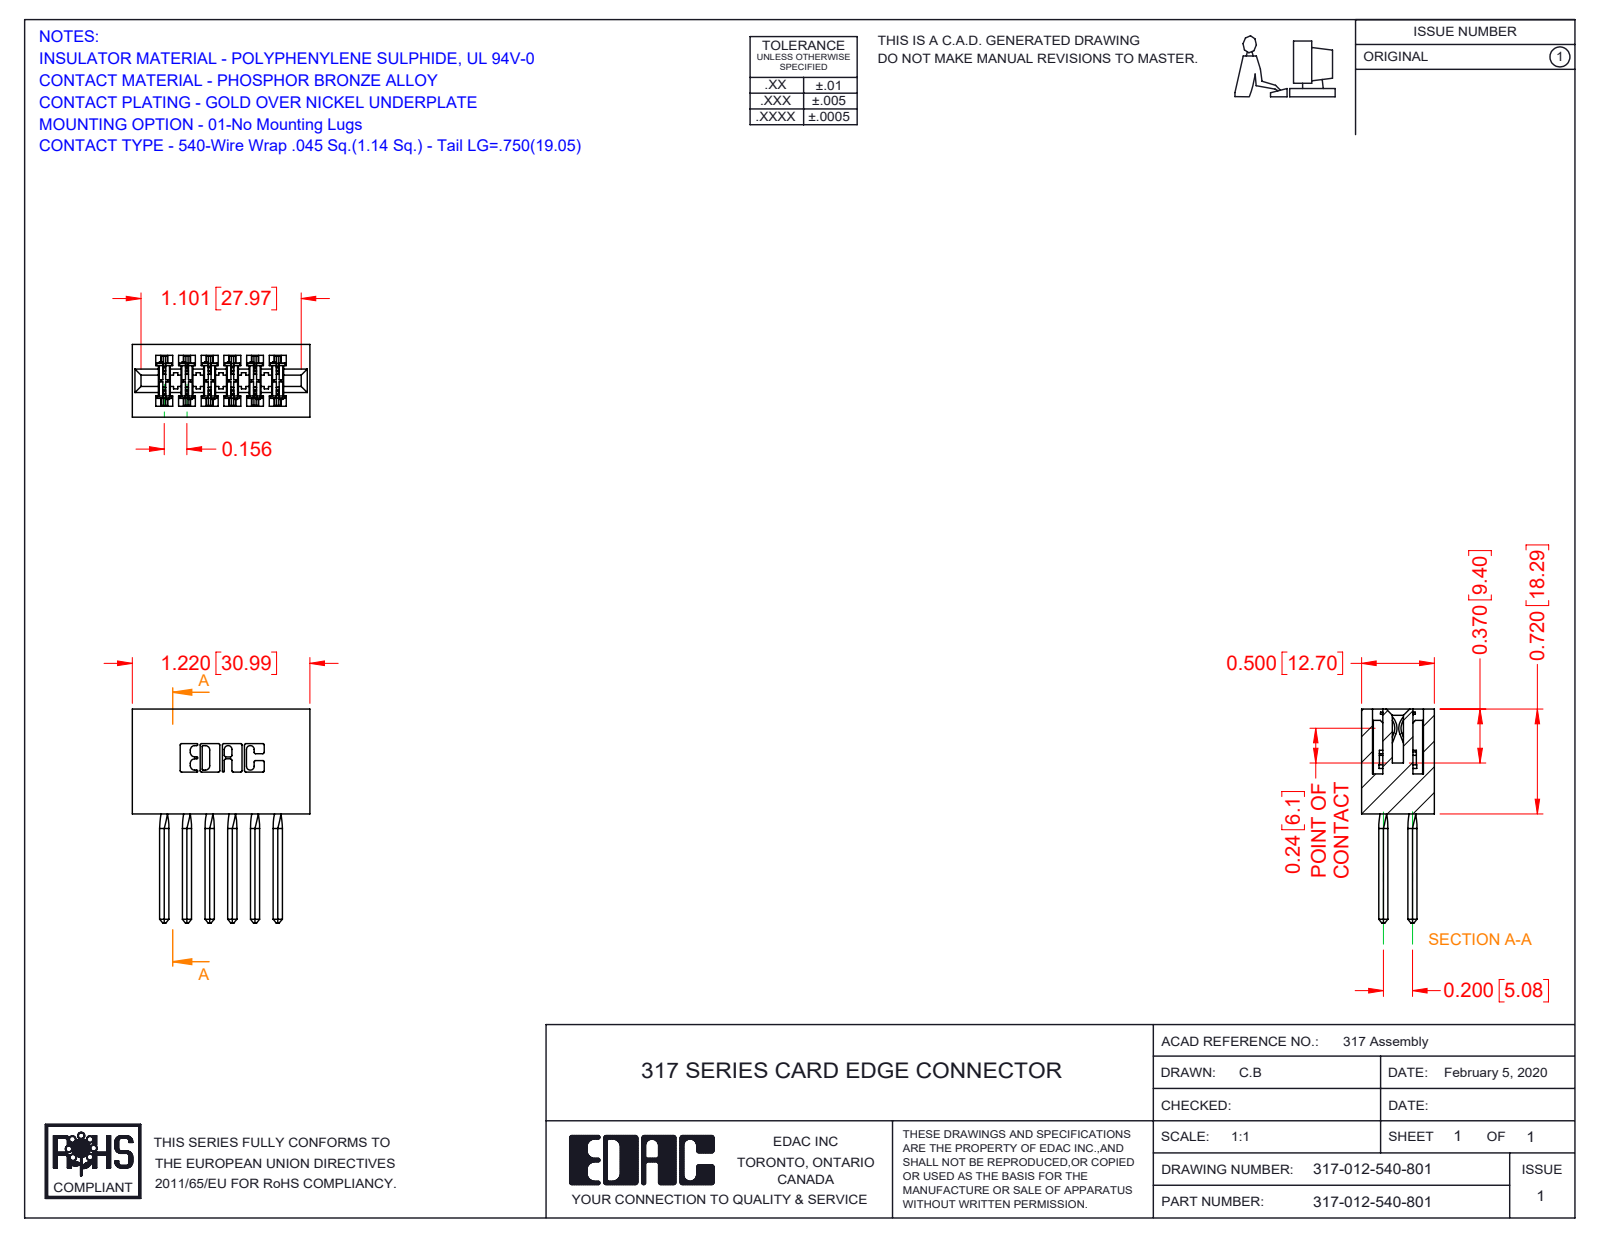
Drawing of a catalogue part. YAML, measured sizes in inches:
part_name: "317-012-540-801; 317-290-001_540; 317 Part_Lugless"
step_written_by: "SolidWorks 2016 (CONFIG_CONTROL_DESIGN)"
units: inches
bodies: {solids: 13, faces: 1158, planar: 926, cylindrical: 184, other: 48}
overall_size: [1.47, 1.22, 0.5]
volume: 0.353
surface_area: 11.64
partial_cylinders:
  - {radius: 0.015, count: 24}
  - {radius: 0.01, count: 22}
  - {radius: 0.007, count: 6}
  - {radius: 0.031, count: 6}
  - {radius: 0.026, count: 3}
  - {radius: 0.095, count: 2}
  - {radius: 0.1, count: 2}
  - {radius: 0.11, count: 2}
face_to_face_distances: [0.11, 0.5, 0.075, 0.425, 0.156, 0.22, 0.065, 0.116, 0.331, 0.141]
